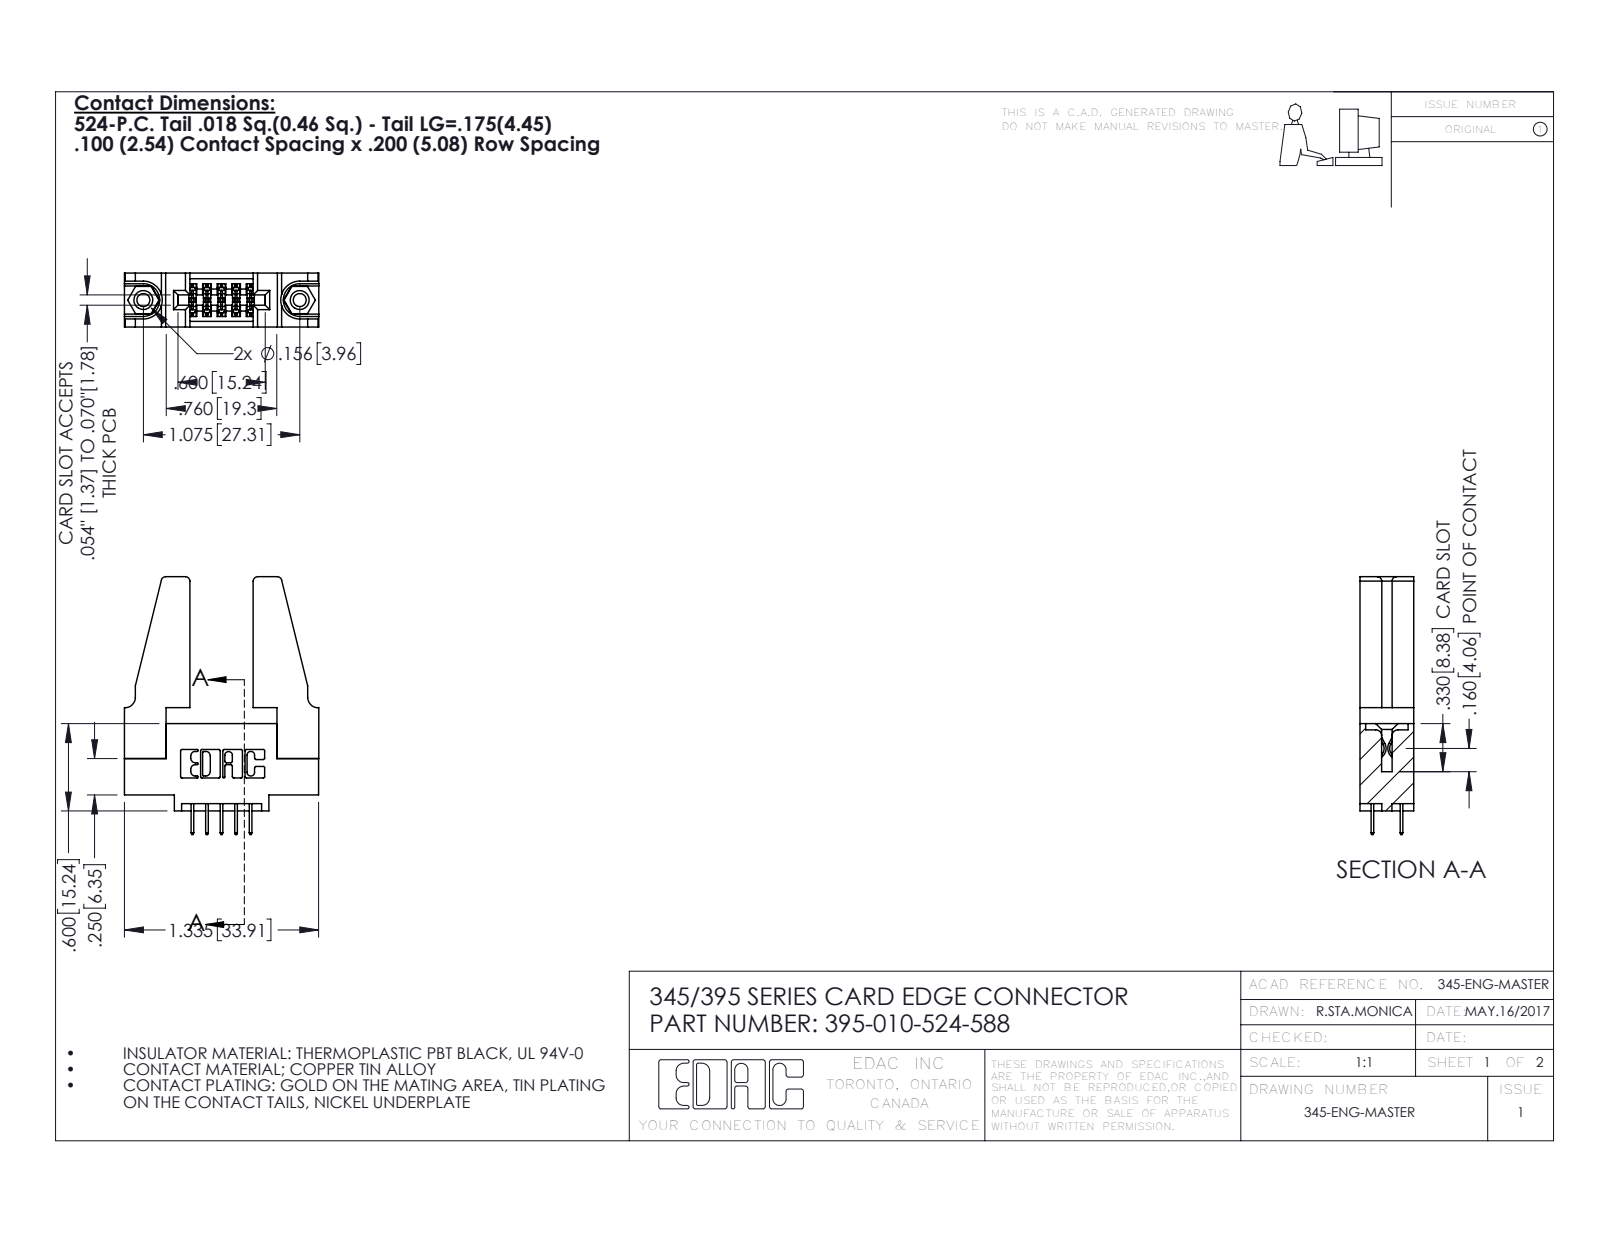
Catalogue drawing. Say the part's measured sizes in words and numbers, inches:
The part is named "395-010-524-588; 345-220-078_345-220-088; 345-250-001_345-250-001-102; 345 Part_0.110 Offset - 0.156 Dia-TH (+1 more)". Its 3-D file was written by "SolidWorks 2016 (CONFIG_CONTROL_DESIGN)". It is 15 solids with 794 faces: 546 planar, 232 cylindrical and 16 other. Overall it measures 1.772 by 1.336 by 0.37 inches. Its volume is 0.373 cubic inches and its surface area 10.37 square inches. Round holes: 2 of diameter 0.089, 2 of diameter 0.125, 2 of diameter 0.156, 1 of diameter 0.064. Round bosses or shafts: 2 of diameter 0.155. Partial cylindrical surfaces (rounded edges, fillets, slot ends): 22 of radius 0.01, 15 of radius 0.006, 8 of radius 0.03, 6 of radius 0.007, 6 of radius 0.031, 3 of radius 0.026, 2 of radius 0.014, 2 of radius 0.019. The main face-to-face distances are 0.37, 0.072, 0.298, 0.2, 0.148, 0.15, 0.22, 0.077, 0.45, 0.287. The hole center spacings are 0.27, 0.847, 1.075.
